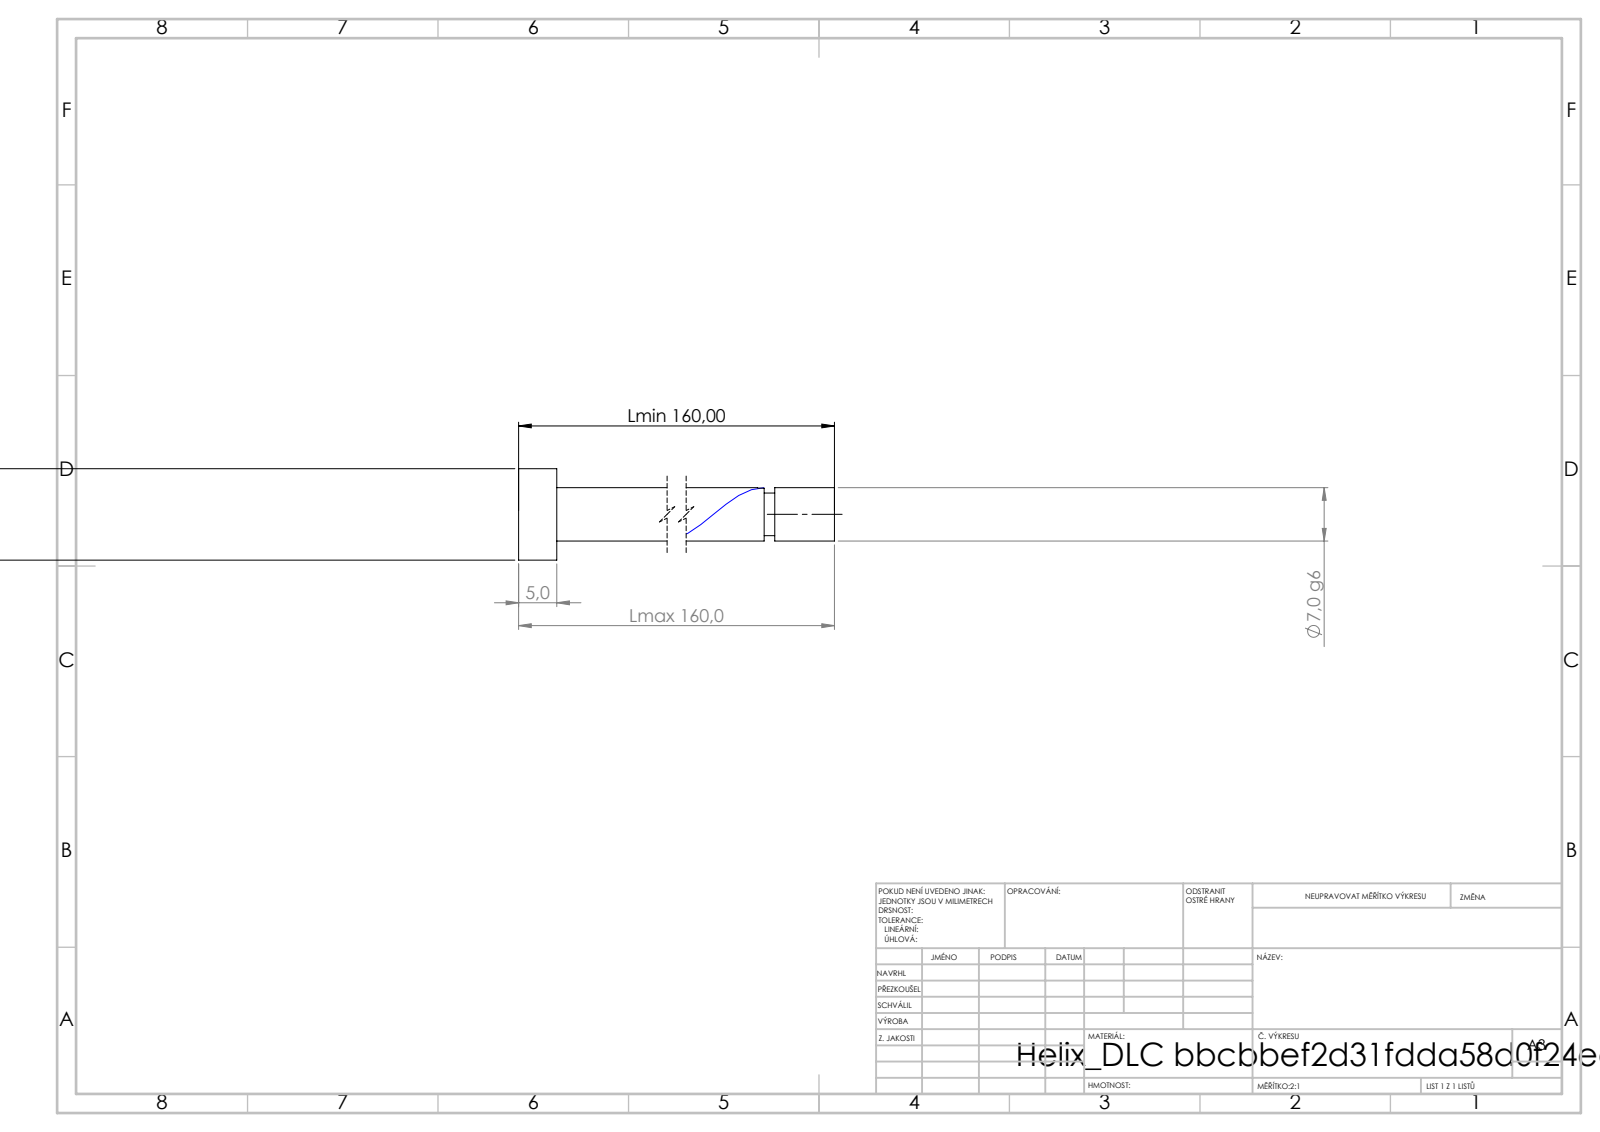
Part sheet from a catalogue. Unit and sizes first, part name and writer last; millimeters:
Units: millimetres
Overall size (bounding box): 160 × 12 × 12
Round bosses / shafts (diameter × count): ⌀12 ×1, ⌀7 ×1, ⌀5.6 ×1
Main face-to-face distances: 5, 160, 155, 152.17, 147.17, 7.83, 150.77, 145.77, 1.4, 9.23
Volume: 6 452 mm³ · Surface area: 3 921 mm²
Bodies: 1 solid, 21 faces (6 planar, 14 cylindrical, 1 other)
STEP written by: SolidWorks 2019 (CONFIG_CONTROL_DESIGN)
